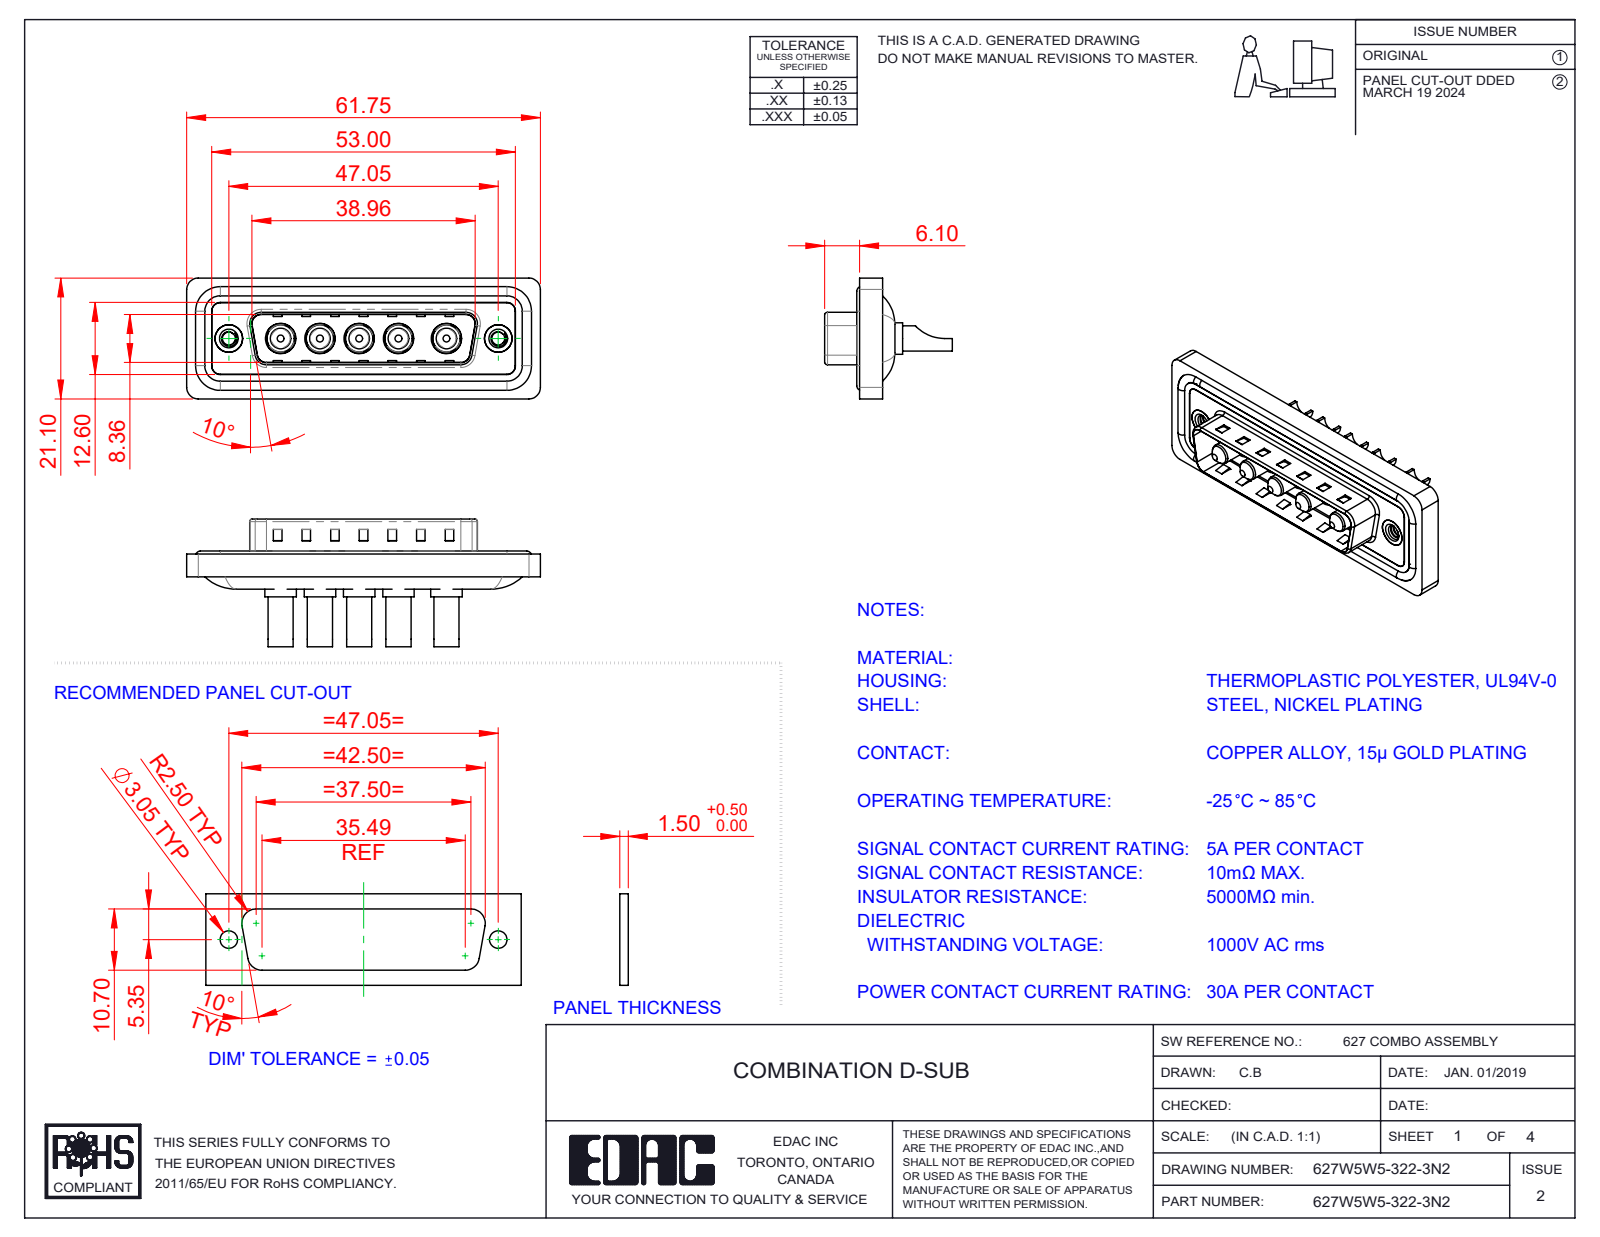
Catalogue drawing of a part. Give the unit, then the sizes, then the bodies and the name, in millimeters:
Units: millimetres
Overall size (bounding box): 61.75 × 22.3 × 21.1
Round holes (diameter × count): ⌀3.5 ×5, ⌀4.85 ×5, ⌀5.3 ×5, ⌀2.26 ×2, ⌀4 ×2, ⌀4.8 ×2, ⌀5 ×2
Round bosses / shafts (diameter × count): ⌀5.5 ×5, ⌀5.2 ×5, ⌀4.75 ×5, ⌀4.4 ×5, ⌀3.75 ×5, ⌀3.6 ×5, ⌀1.6 ×4, ⌀4.9 ×2
Partial cylindrical surfaces — rounded edges, fillets, slot ends (radius × count): R1.5 ×22, R2 ×18, R0.5 ×8, R1.6 ×8, R2.1 ×5, R0.25 ×4, R0.6 ×4, R0.65 ×4
Main face-to-face distances: 0.4, 1.5, 0.5, 1.1, 3.1, 1.6, 2.9, 0.82, 9.58, 5.65
Hole centre spacings: 6.86, 9.04, 13.73, 38.01, 6.87, 8.37, 8.38, 9.05
Volume: 7 593 mm³ · Surface area: 12 334 mm²
Bodies: 17 solids, 708 faces (274 planar, 298 cylindrical, 136 other)
Part name (STEP PRODUCT): 627Combo Threaded Rivet_2; 627Combo Housing_5W5; Power Pin_30A SC; 627Combo Shell Front_25 Contacts (+3 more)
STEP written by: SolidWorks 2023 (CONFIG_CONTROL_DESIGN)
